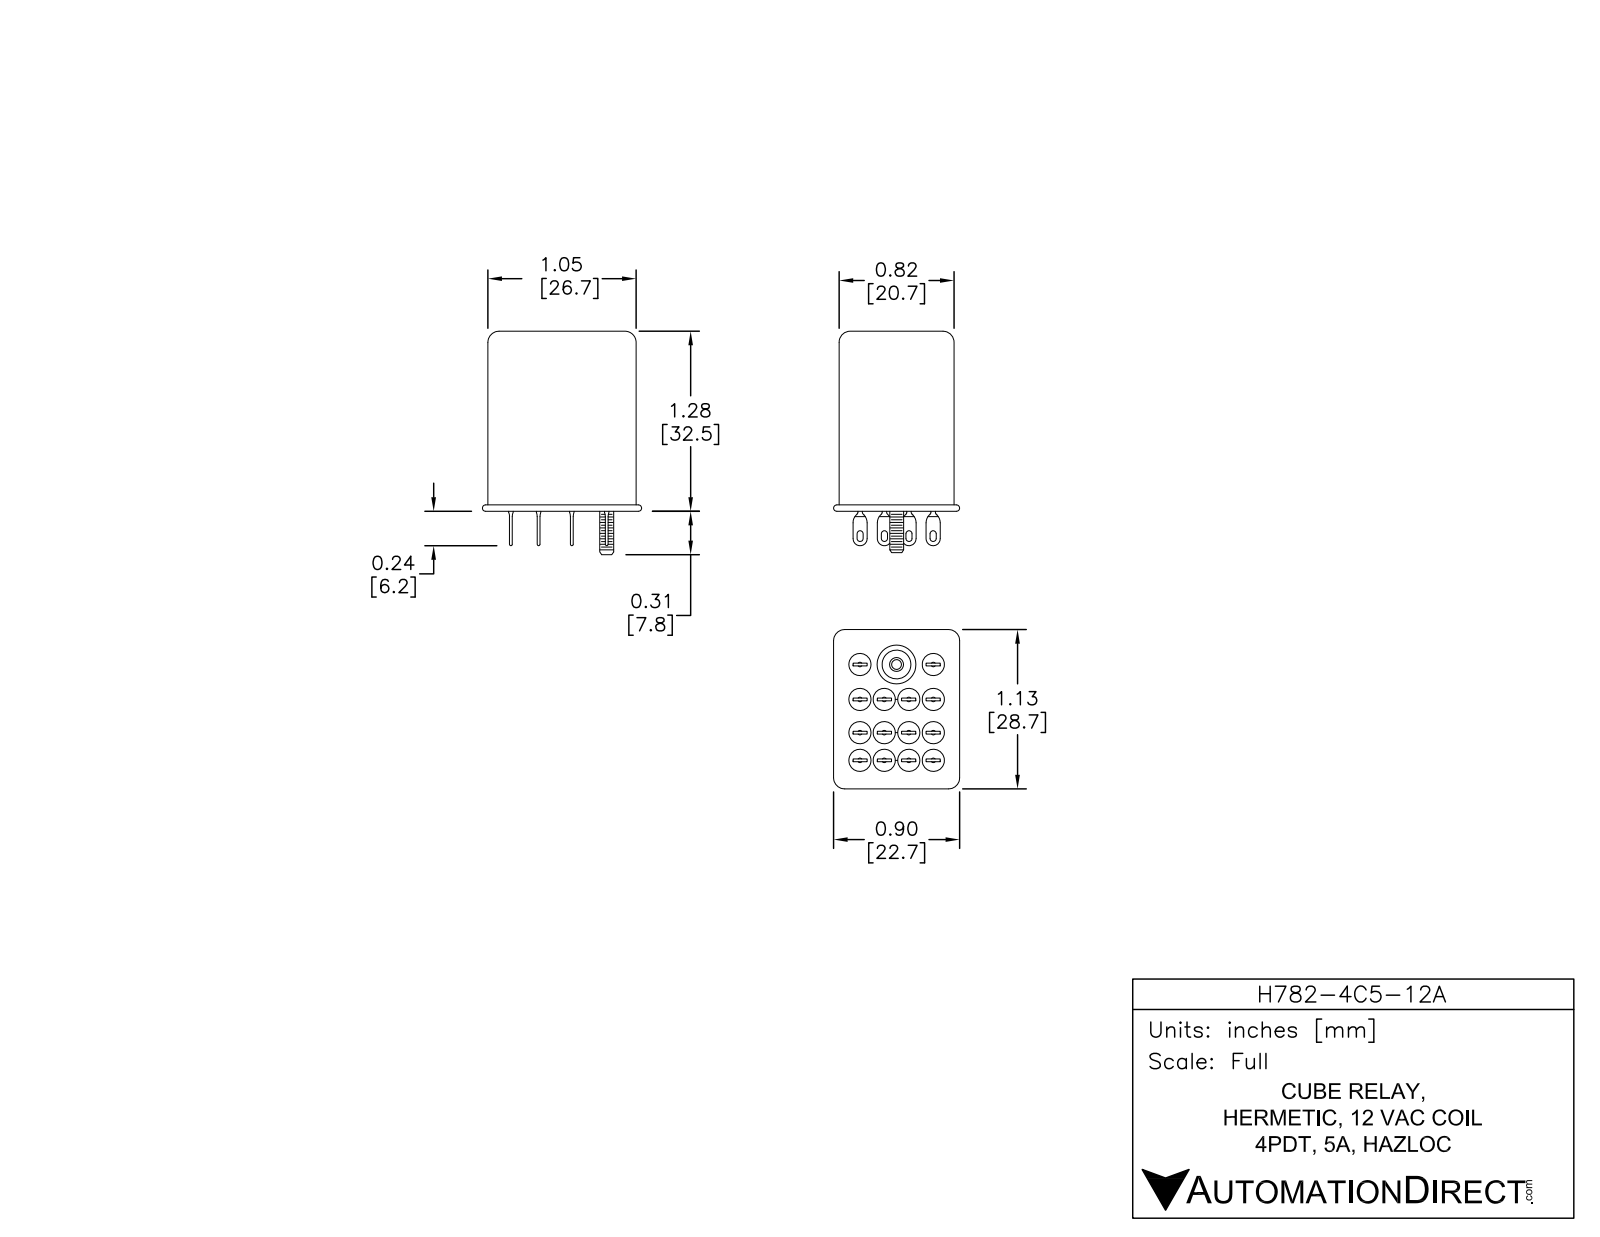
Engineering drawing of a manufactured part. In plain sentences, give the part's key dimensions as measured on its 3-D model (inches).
The part is named "H782-4C5-12A". Its 3-D file was written by "SolidWorks 2013 (AUTOMOTIVE_DESIGN)". It is 2 solids with 408 faces: 186 planar, 178 cylindrical and 44 other. Overall it measures 1.383 by 1.134 by 0.902 inches. Its volume is 0.931 cubic inches and its surface area 6.406 square inches. Round holes: 1 of diameter 0.236. Round bosses or shafts: 14 of diameter 0.124, 1 of diameter 0.094. Partial cylindrical surfaces (rounded edges, fillets, slot ends): 56 of radius 0.004, 36 of radius 0.02, 8 of radius 0.008, 4 of radius 0.079. The main face-to-face distances are 0.807, 1.087, 1.043, 1.087, 0.205, 0.016, 0.409, 0.394, 0.189, 0.22.
